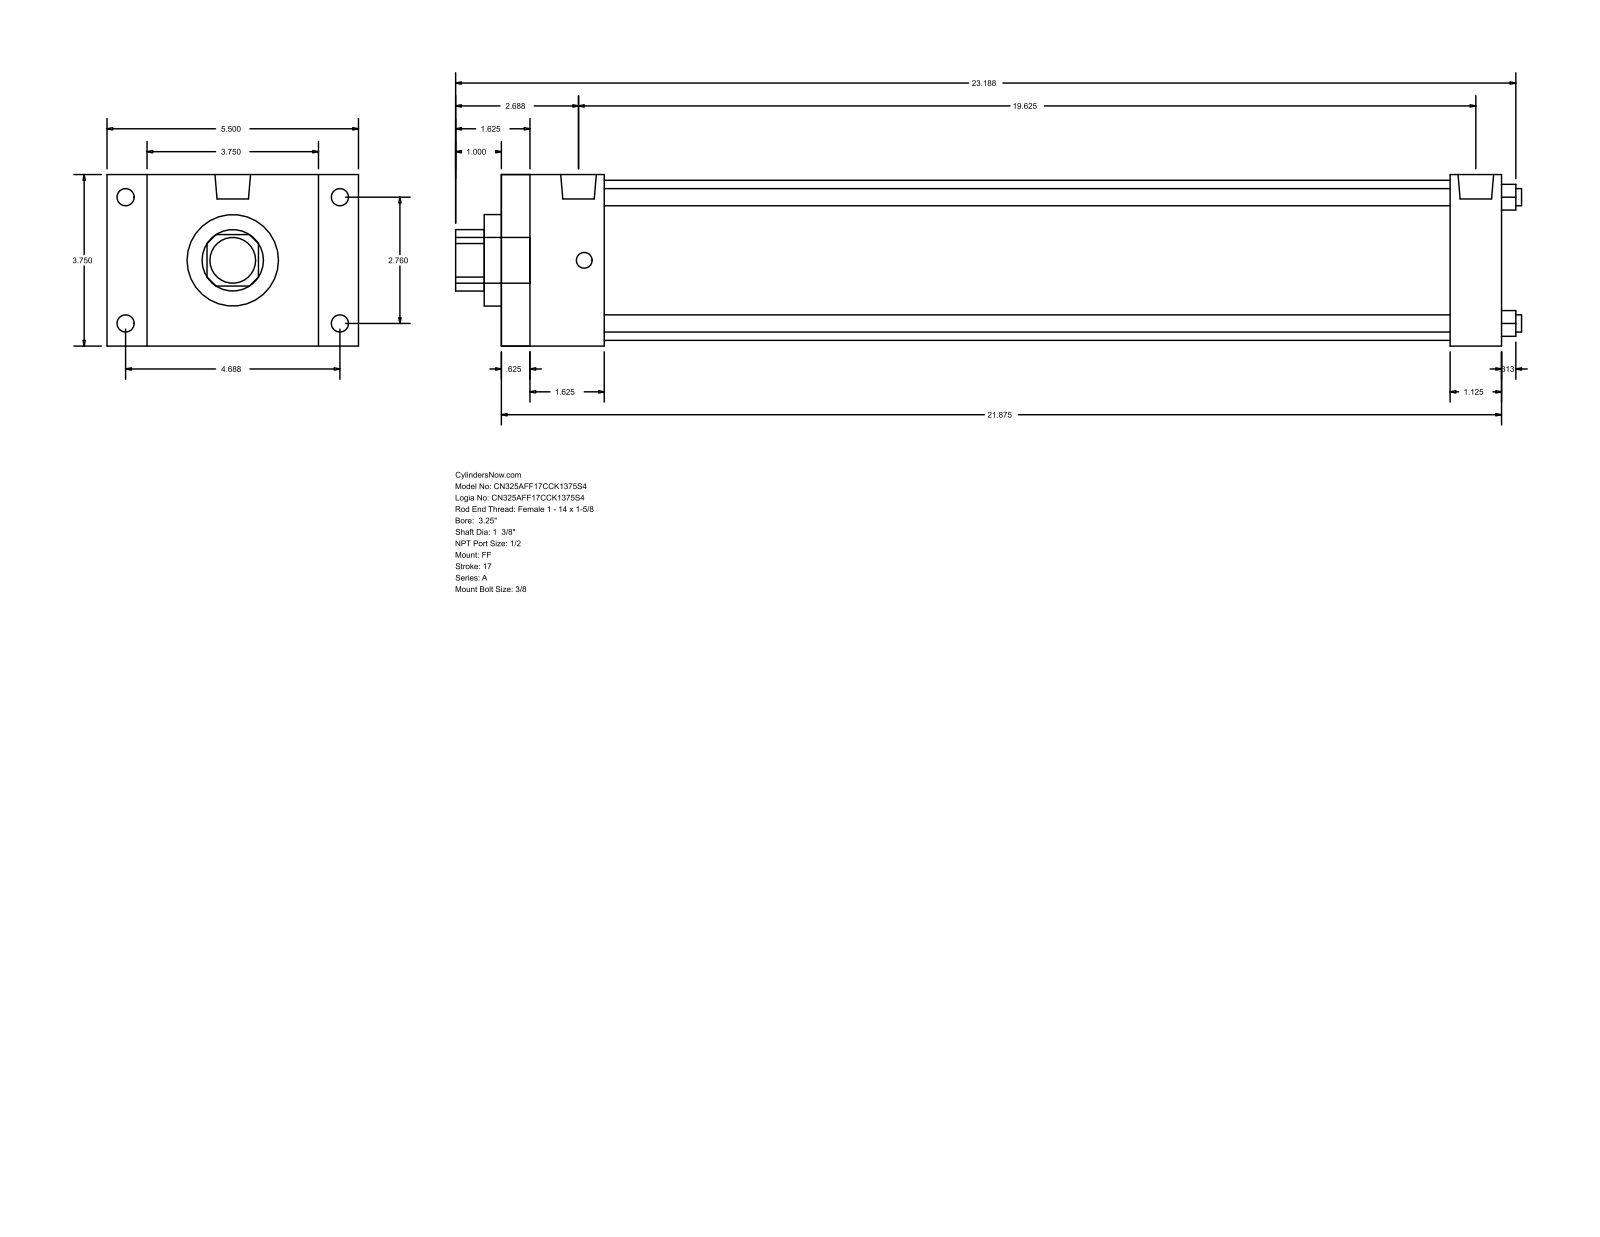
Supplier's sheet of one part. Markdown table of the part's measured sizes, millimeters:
| quantity | value |
| --- | --- |
| part name | A_FF__0325_1.375 |
| STEP written by | GSSL Pune (CONFIG_CONTROL_DESIGN) |
| units | millimeters |
| bodies | 0 solids, 92 faces (64 planar, 28 cylindrical, 0 other) |
| overall size | 592.14 × 139.7 × 95.25 |
| round holes (diameter × count) | 9.53 × 4, 34.92 × 1, 50.8 × 1, 88.9 × 1 |
| round bosses / shafts (diameter × count) | 9.53 × 4, 8.73 × 4, 19.77 × 2, 25.4 × 1 |
| partial cylindrical surfaces (radius × count) | 17.06 × 1 |
| main face-to-face distances | 95.24, 555.62, 539.75, 15.87, 22.23, 117.47, 28.57, 57.15, 527.05, 41.28 |
| hole center spacings | 49.57, 70.1, 99.14 |
